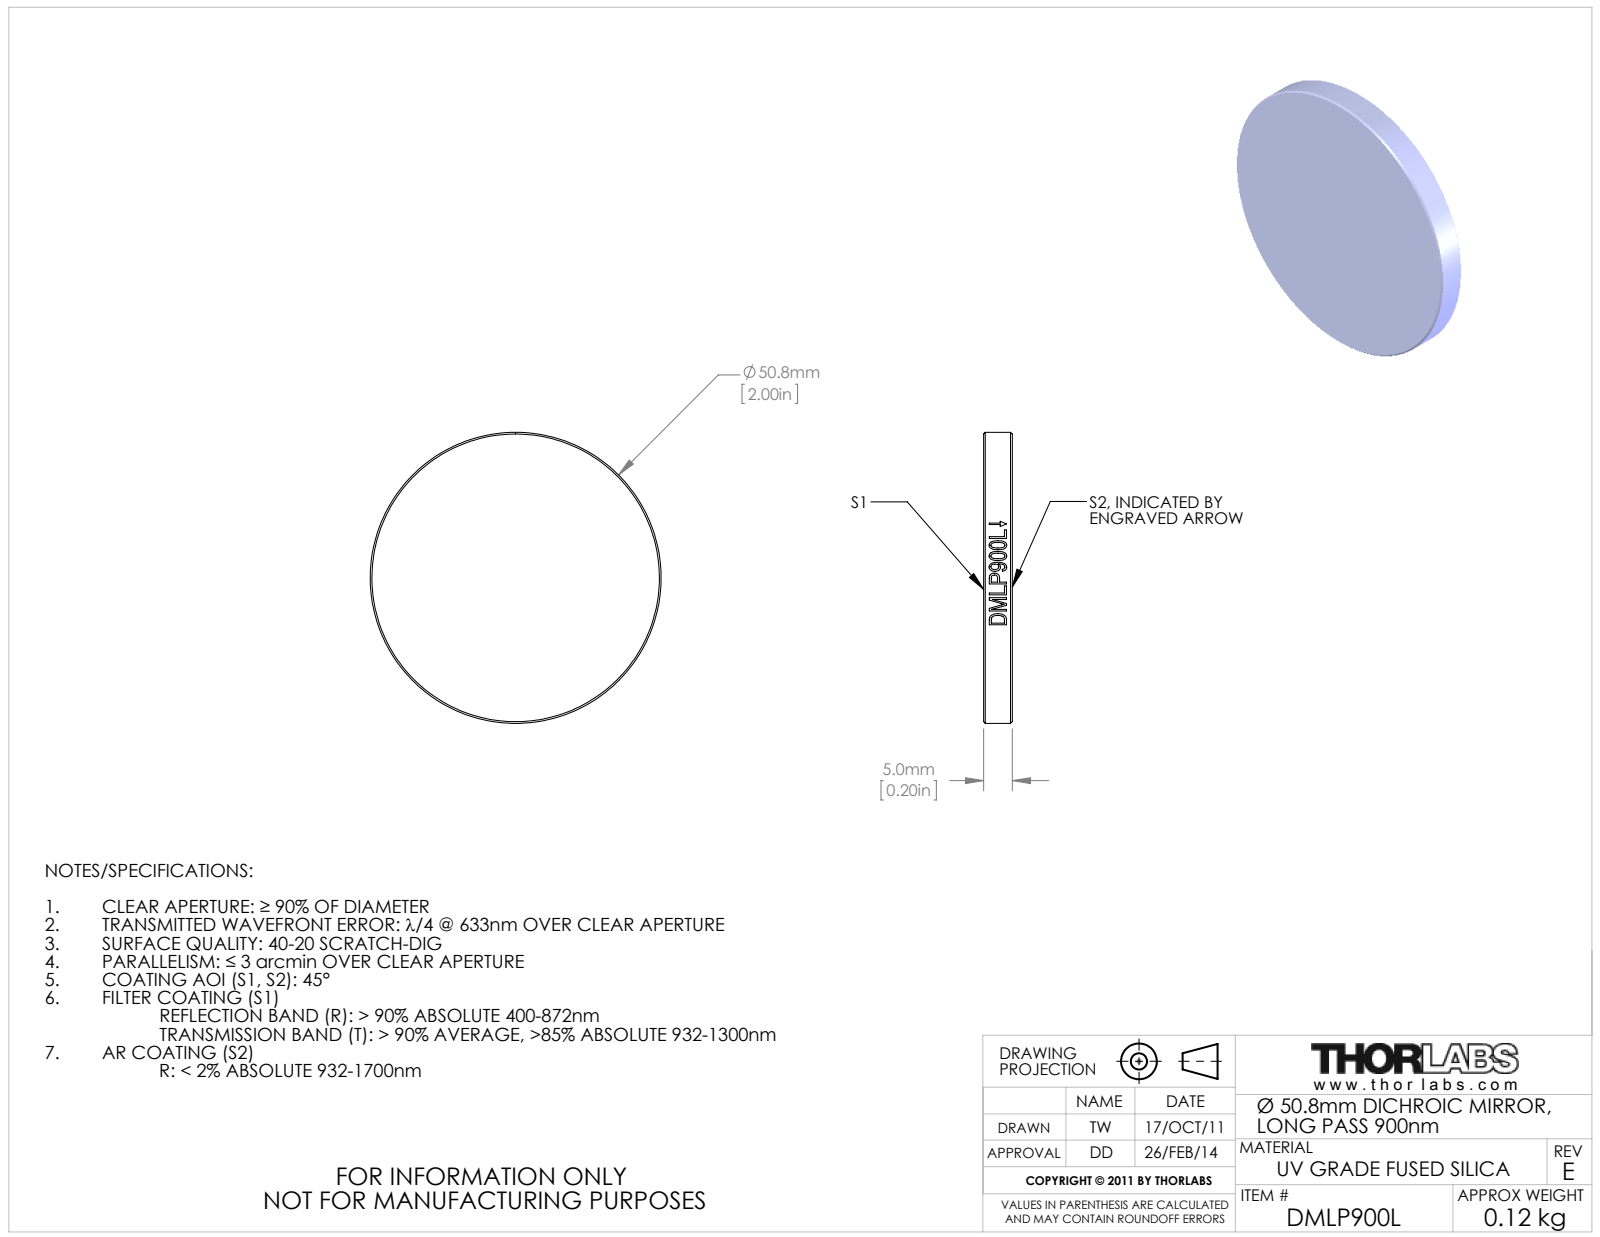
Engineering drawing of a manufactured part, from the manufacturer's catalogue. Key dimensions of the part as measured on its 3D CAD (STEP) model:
Part name (STEP PRODUCT): 21031-E0W
STEP written by: SolidWorks 2011 (CONFIG_CONTROL_DESIGN)
Units: millimetres
Bodies: 0 solids, 22 faces (2 planar, 16 cylindrical, 4 other)
Overall size (bounding box): 50.8 × 50.8 × 5
Round bosses / shafts (diameter × count): ⌀50.8 ×1
Main face-to-face distances: 5
